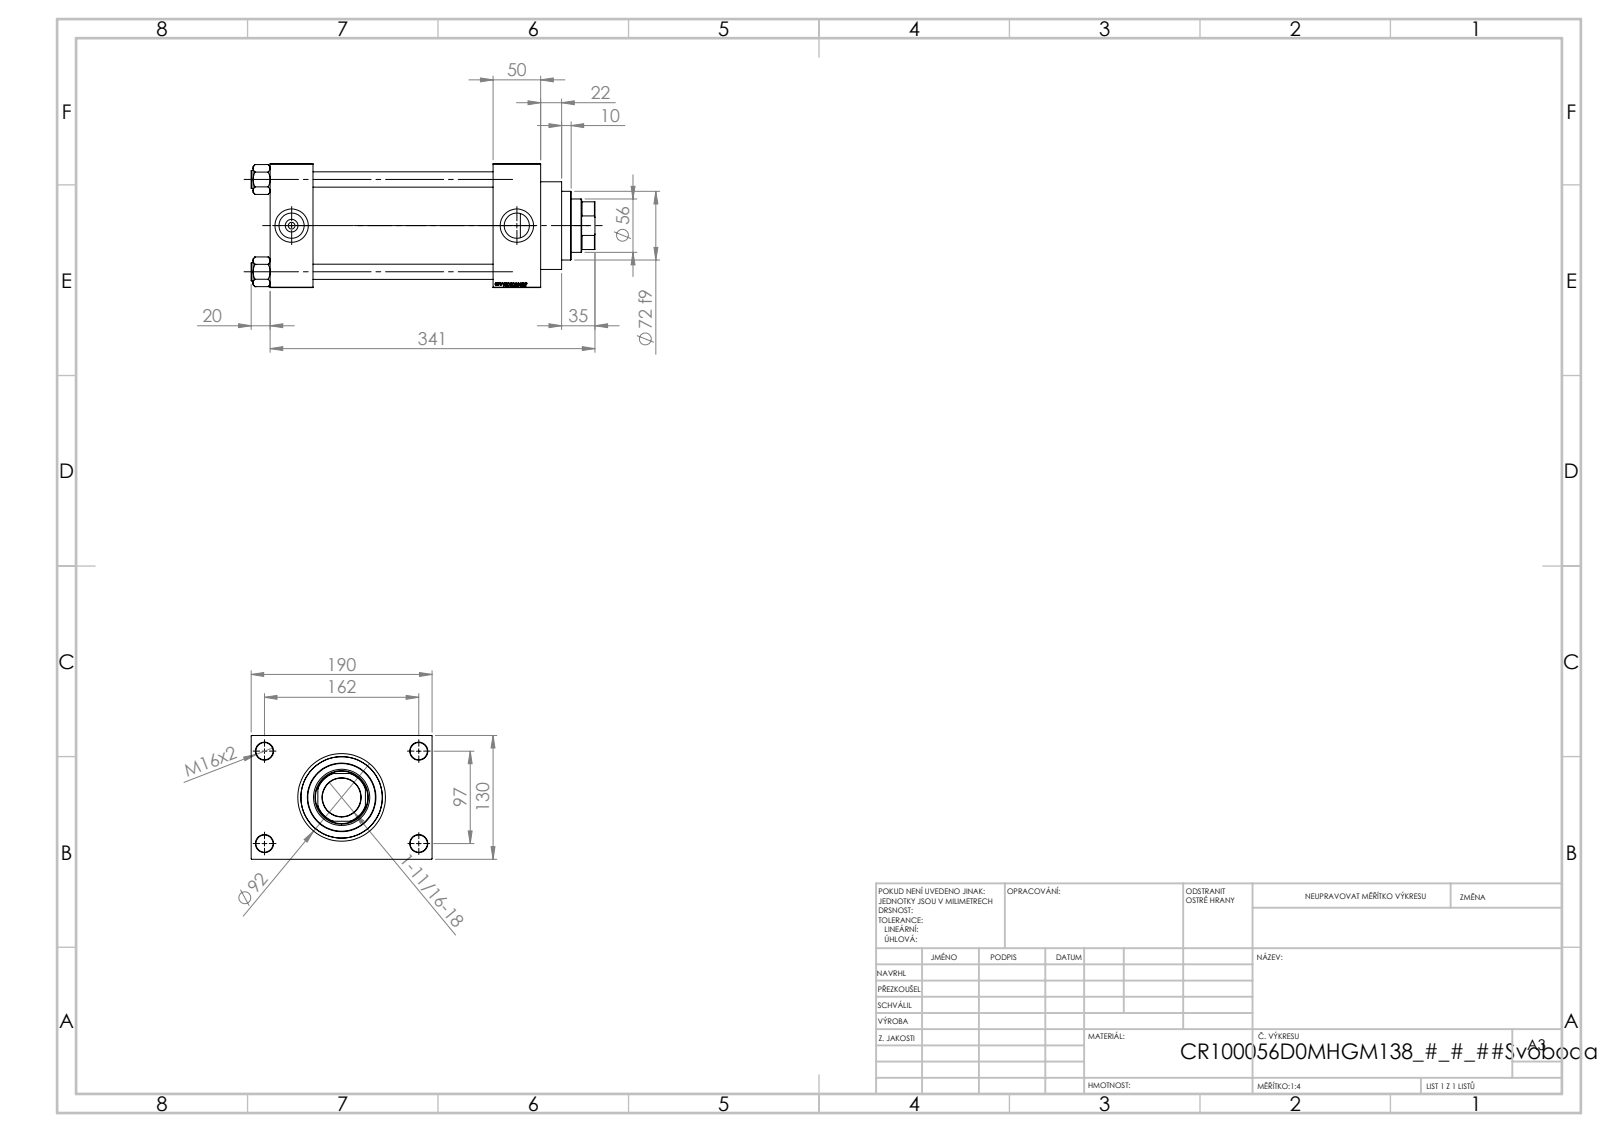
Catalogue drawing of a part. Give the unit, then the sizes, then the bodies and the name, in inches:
Units: inches
Overall size (bounding box): 14.213 × 7.48 × 5.118
Round holes (diameter × count): ⌀0.63 ×4, ⌀0.709 ×4, ⌀0.276 ×2, ⌀1.041 ×2, ⌀1.378 ×2, ⌀1.594 ×1, ⌀2.205 ×1, ⌀2.323 ×1, ⌀2.992 ×1, ⌀3.366 ×1, ⌀3.937 ×1
Round bosses / shafts (diameter × count): ⌀0.748 ×4, ⌀4.173 ×1, ⌀3.622 ×1, ⌀2.835 ×1
Partial cylindrical surfaces — rounded edges, fillets, slot ends (radius × count): R1.063 ×1
Main face-to-face distances: 5.118, 1.969, 1.772, 9.213, 7.441, 11.181, 9.409, 1.181, 6.299, 7.402
Hole centre spacings: 1.281, 2.698, 3.717, 3.815, 4.026, 5.096, 6.367, 3.819
Volume: 190.9 in³ · Surface area: 749 in²
Bodies: 11 solids, 1151 faces (545 planar, 88 cylindrical, 518 other)
Part name (STEP PRODUCT): V215_VC_A; NUT_M5_D; V215CR_VCP_D; V215CR_D_TYCINKA (+1 more)
STEP written by: SolidWorks 2019 (CONFIG_CONTROL_DESIGN)
